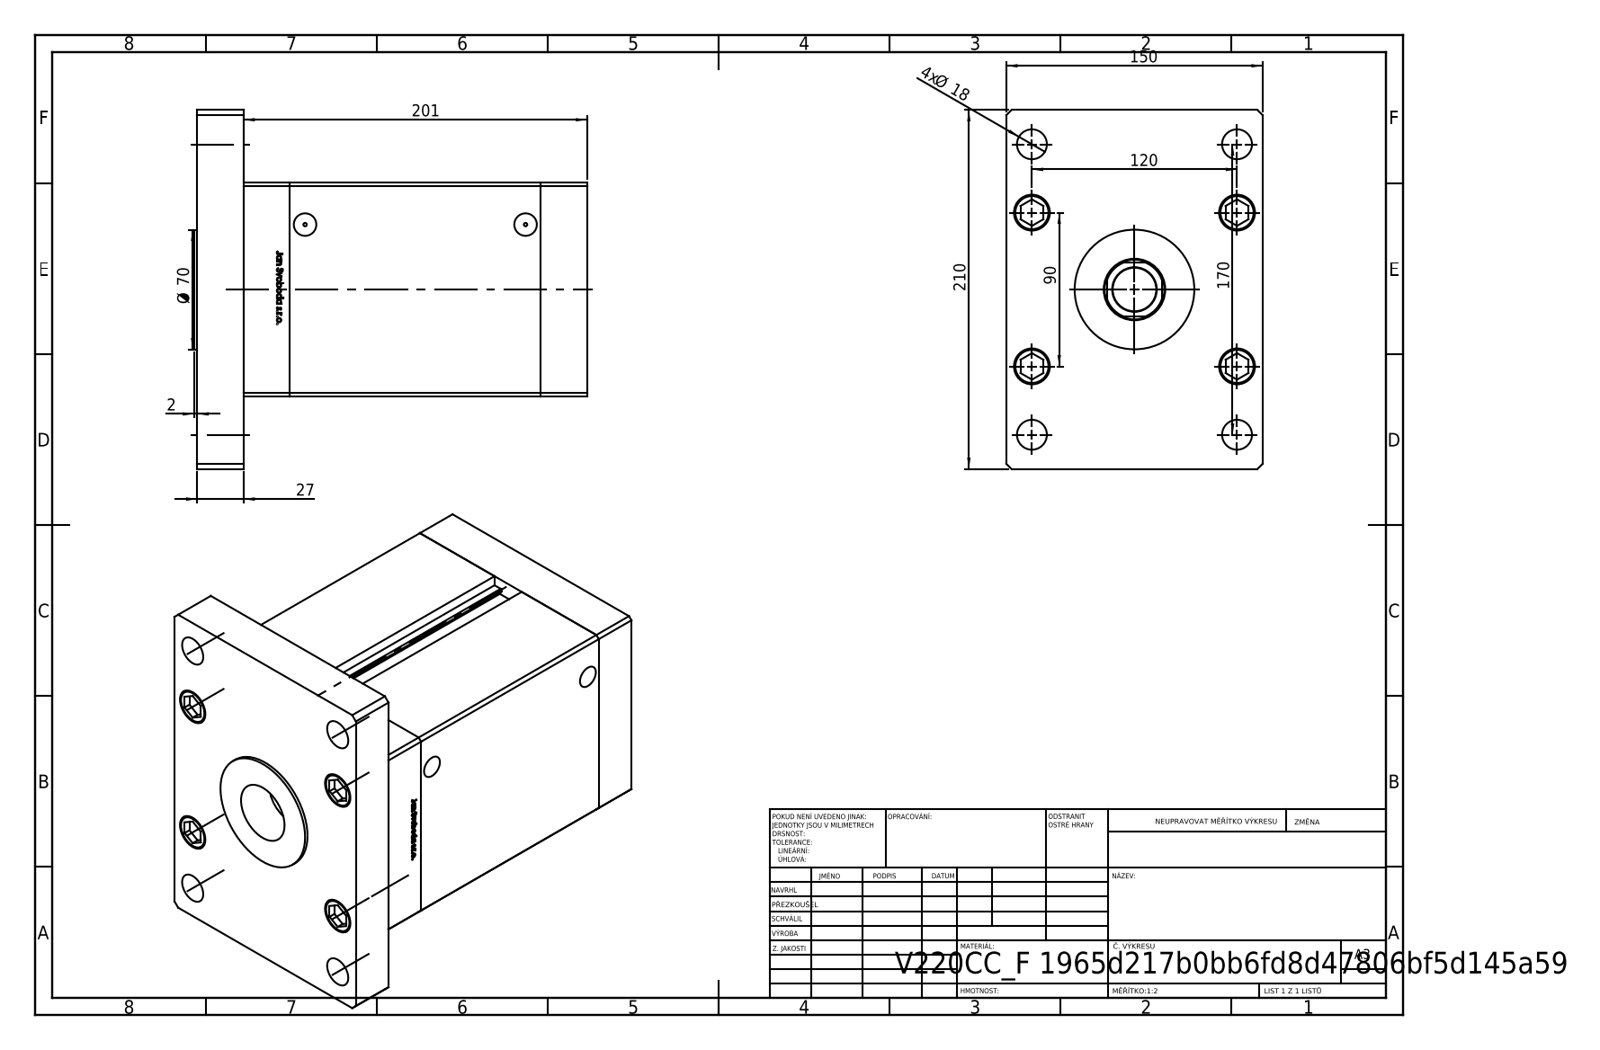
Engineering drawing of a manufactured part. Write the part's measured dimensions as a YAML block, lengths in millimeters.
part_name: "V220C BACK_F; V220C_VC_F; V220C_FRONT_F; V220C_F (+2 more)"
step_written_by: "SolidWorks 2019 (CONFIG_CONTROL_DESIGN)"
units: millimeters
bodies: {solids: 19, faces: 1308, planar: 515, cylindrical: 187, other: 606}
overall_size: [230, 210, 150]
volume: 3992000
surface_area: 445989
round_holes:
  - {diameter: 17.5, count: 9}
  - {diameter: 22, count: 5}
  - {diameter: 16, count: 4}
  - {diameter: 21, count: 4}
  - {diameter: 2, count: 2}
  - {diameter: 13.16, count: 2}
  - {diameter: 25.5, count: 1}
  - {diameter: 36, count: 1}
  - {diameter: 37.5, count: 1}
round_bosses_or_shafts:
  - {diameter: 8, count: 9}
  - {diameter: 21, count: 5}
  - {diameter: 80, count: 1}
  - {diameter: 70, count: 1}
partial_cylinders:
  - {radius: 0.93, count: 2}
  - {radius: 17.5, count: 1}
face_to_face_distances: [27, 174, 201, 150, 125, 147, 54, 228, 34.8, 7.8]
hole_center_spacings: [51, 40, 75, 104.04, 120, 126.49, 130, 176.92]
